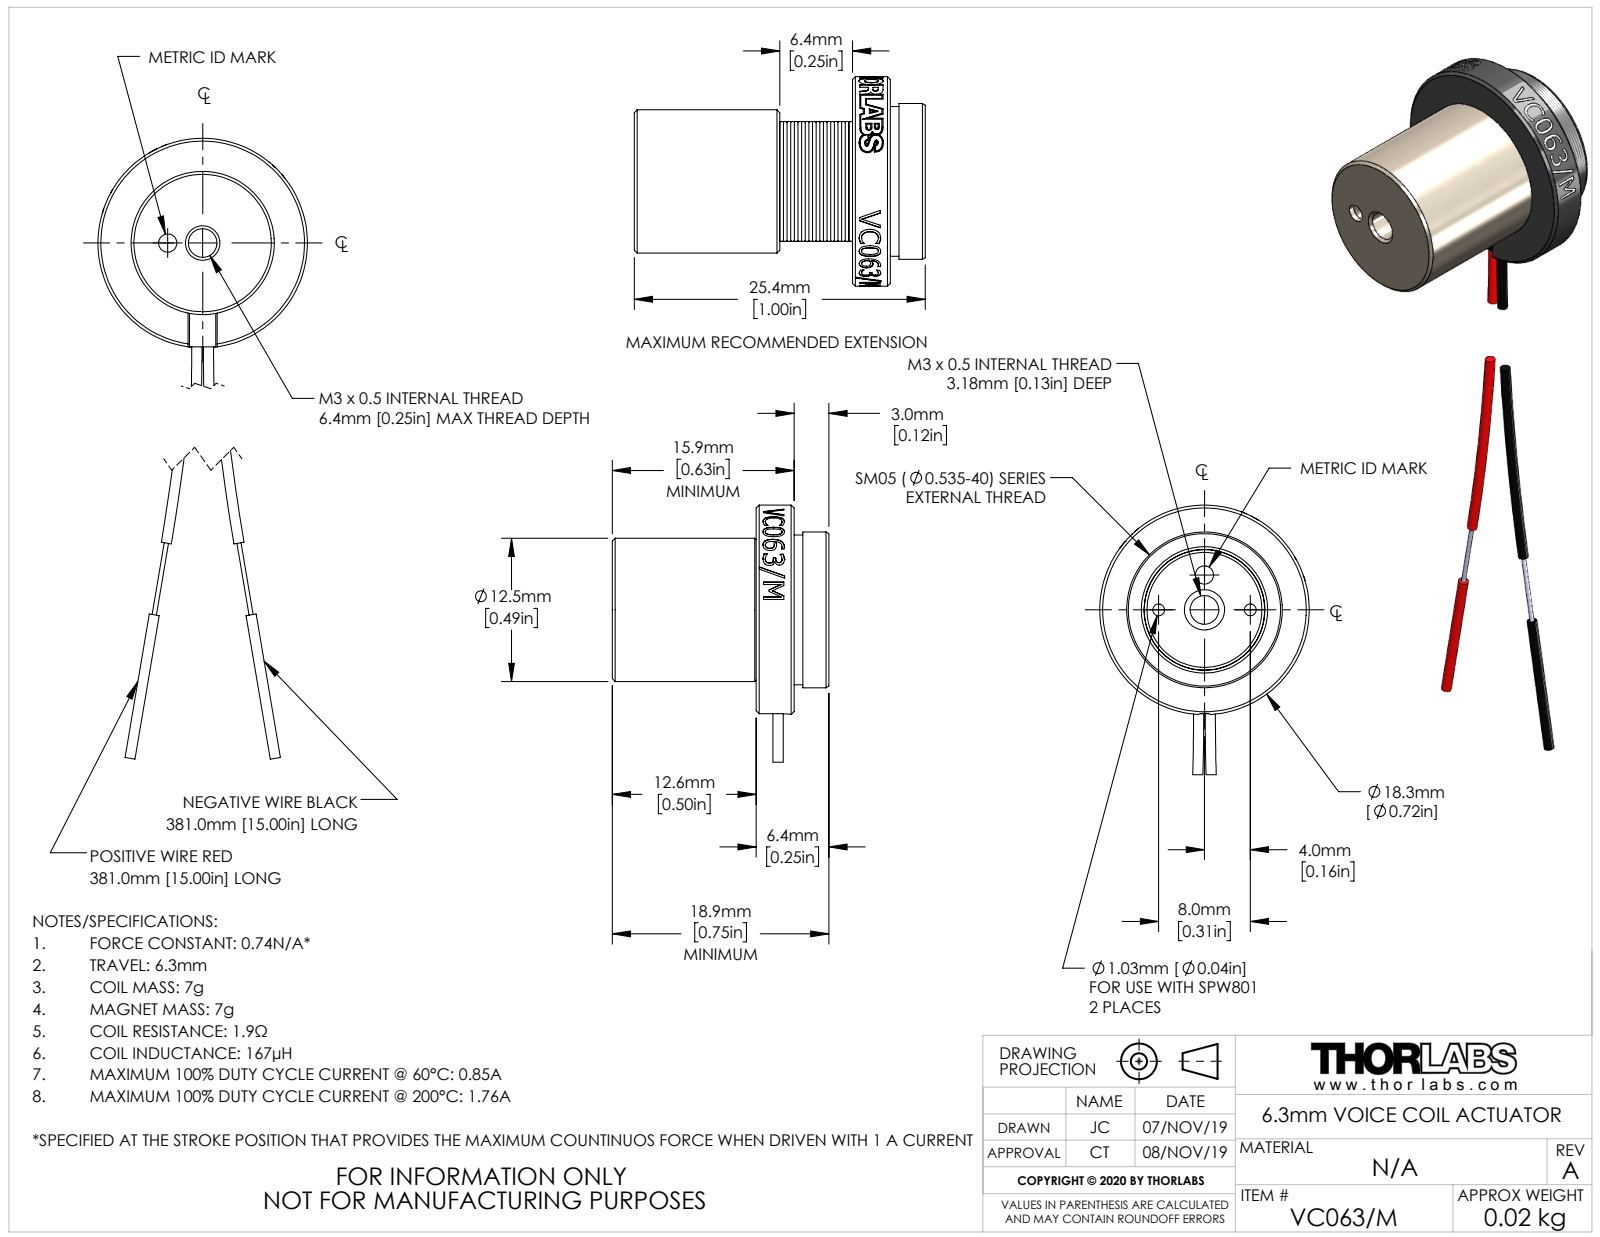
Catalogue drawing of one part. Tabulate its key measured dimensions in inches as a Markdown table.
| quantity | value |
| --- | --- |
| part name | TTN200602-E0W |
| STEP written by | SolidWorks 2018 (AUTOMOTIVE_DESIGN) |
| units | inches |
| bodies | 5 solids, 542 faces (123 planar, 124 cylindrical, 295 other) |
| overall size | 0.745 × 0.72 × 0.719 |
| volume | 0.15 in³ |
| surface area | 5.236 in² |
| round holes (diameter × count) | 0.04 × 2, 0.063 × 2, 0.098 × 1, 0.27 × 1, 0.414 × 1, 0.42 × 1, 0.435 × 1 |
| round bosses / shafts (diameter × count) | 0.72 × 1, 0.535 × 1, 0.515 × 1, 0.492 × 1, 0.415 × 1, 0.415 × 1, 0.412 × 1, 0.406 × 1 |
| partial cylindrical surfaces (radius × count) | 0.05 × 1, 0.359 × 1 |
| main face-to-face distances | 0.37, 0.25, 0.12, 0.5, 0.125, 0.13, 0.62, 0.745, 0.625, 0.495 |
| hole center spacings | 0.12, 0.157, 0.198, 0.037, 0.17, 0.278, 0.315 |
